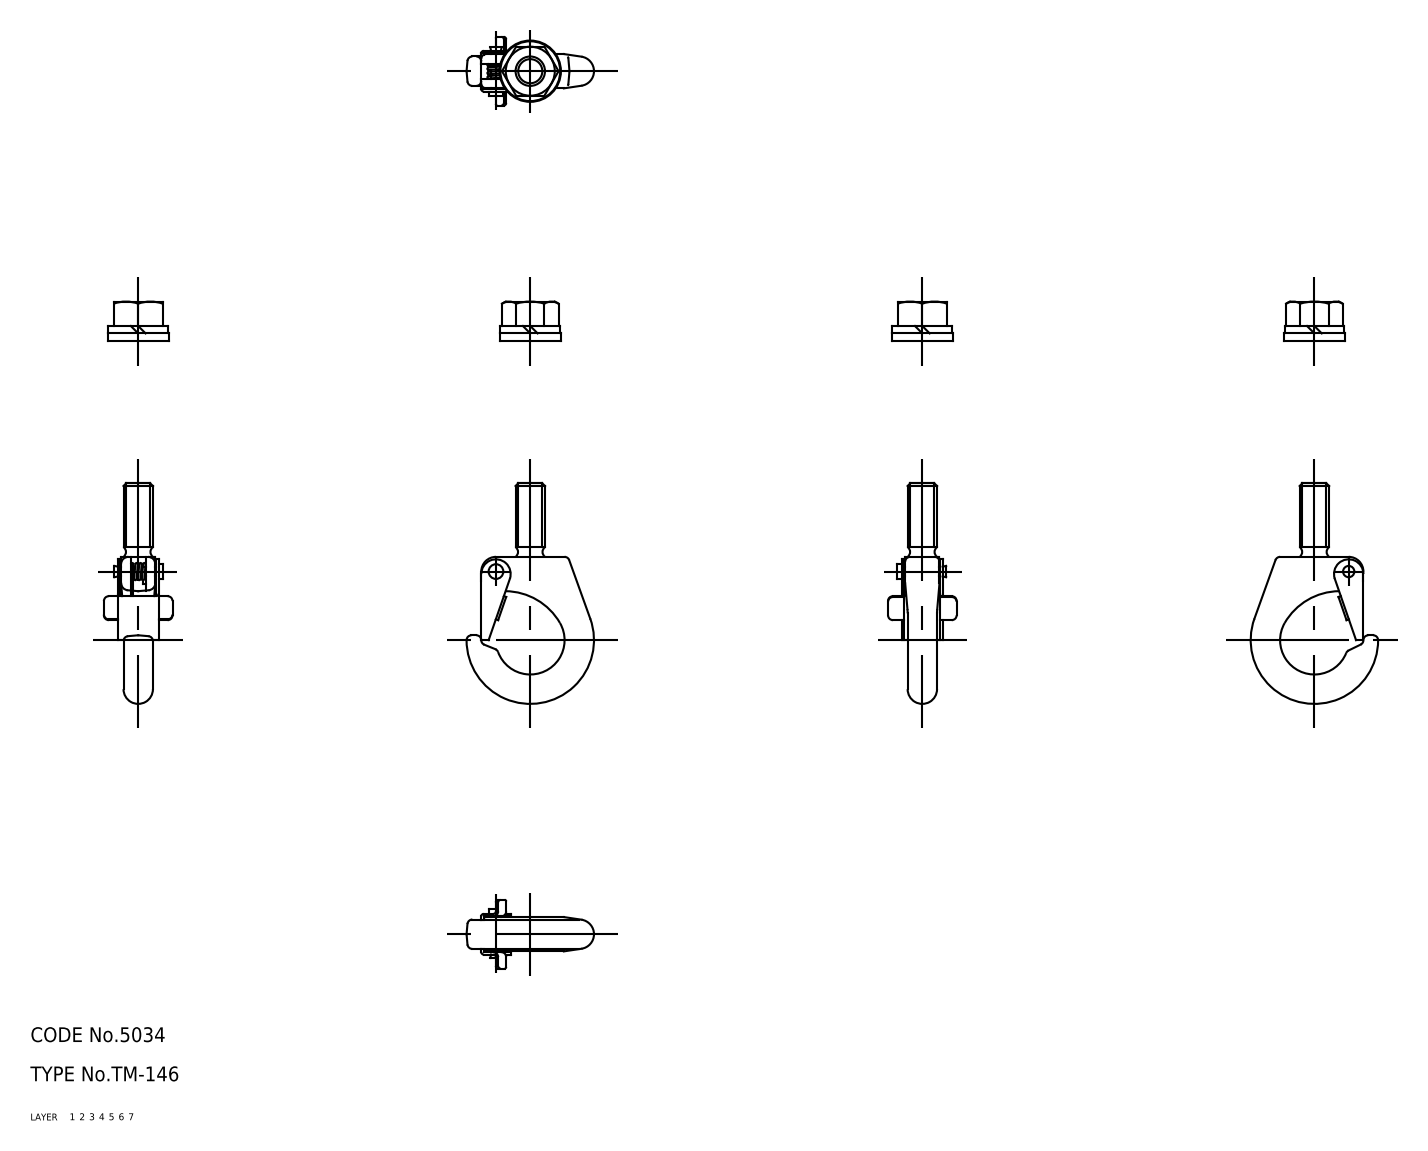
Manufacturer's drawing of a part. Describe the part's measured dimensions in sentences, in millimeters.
The part is named "spring; washer_B; washer_A; stopper (+4 more)". Its 3-D file was written by "CADfix (AUTOMOTIVE_DESIGN)". It is 7 solids with 150 faces: 0 planar, 0 cylindrical and 150 other. Overall it measures 45 by 26 by 14 millimeters. Its volume is 2 982 cubic millimeters and its surface area 3 197 square millimeters.
